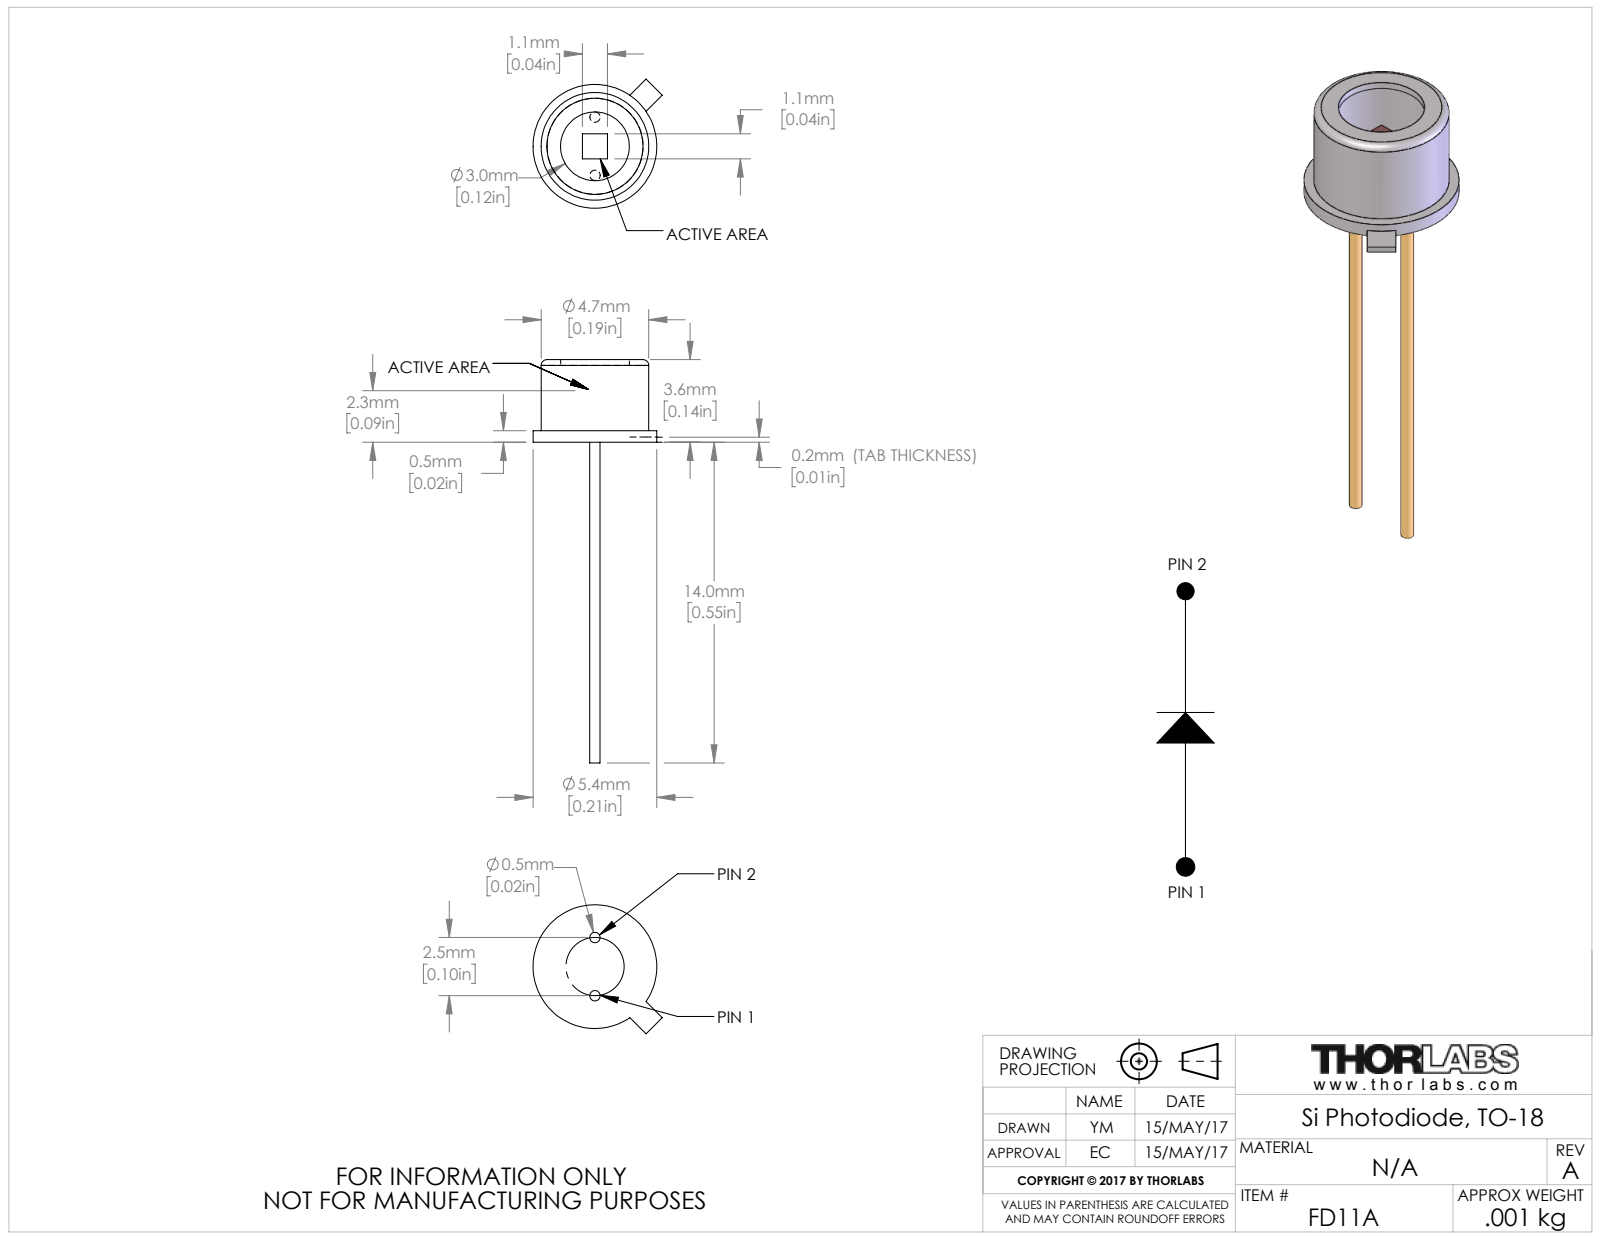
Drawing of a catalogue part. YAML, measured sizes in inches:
part_name: "TTN132079-E0W"
step_written_by: "SolidWorks 2016 (AUTOMOTIVE_DESIGN)"
units: inches
bodies: {solids: 2, faces: 31, planar: 17, cylindrical: 12, other: 2}
overall_size: [0.693, 0.222, 0.222]
volume: 0.002
surface_area: 0.31
round_holes:
  - {diameter: 0.118, count: 1}
  - {diameter: 0.165, count: 1}
round_bosses_or_shafts:
  - {diameter: 0.018, count: 2}
  - {diameter: 0.213, count: 1}
  - {diameter: 0.185, count: 1}
face_to_face_distances: [0.132, 0.122, 0.142, 0.02, 0.112, 0.043, 0.089, 0.079, 0.069, 0.053]
